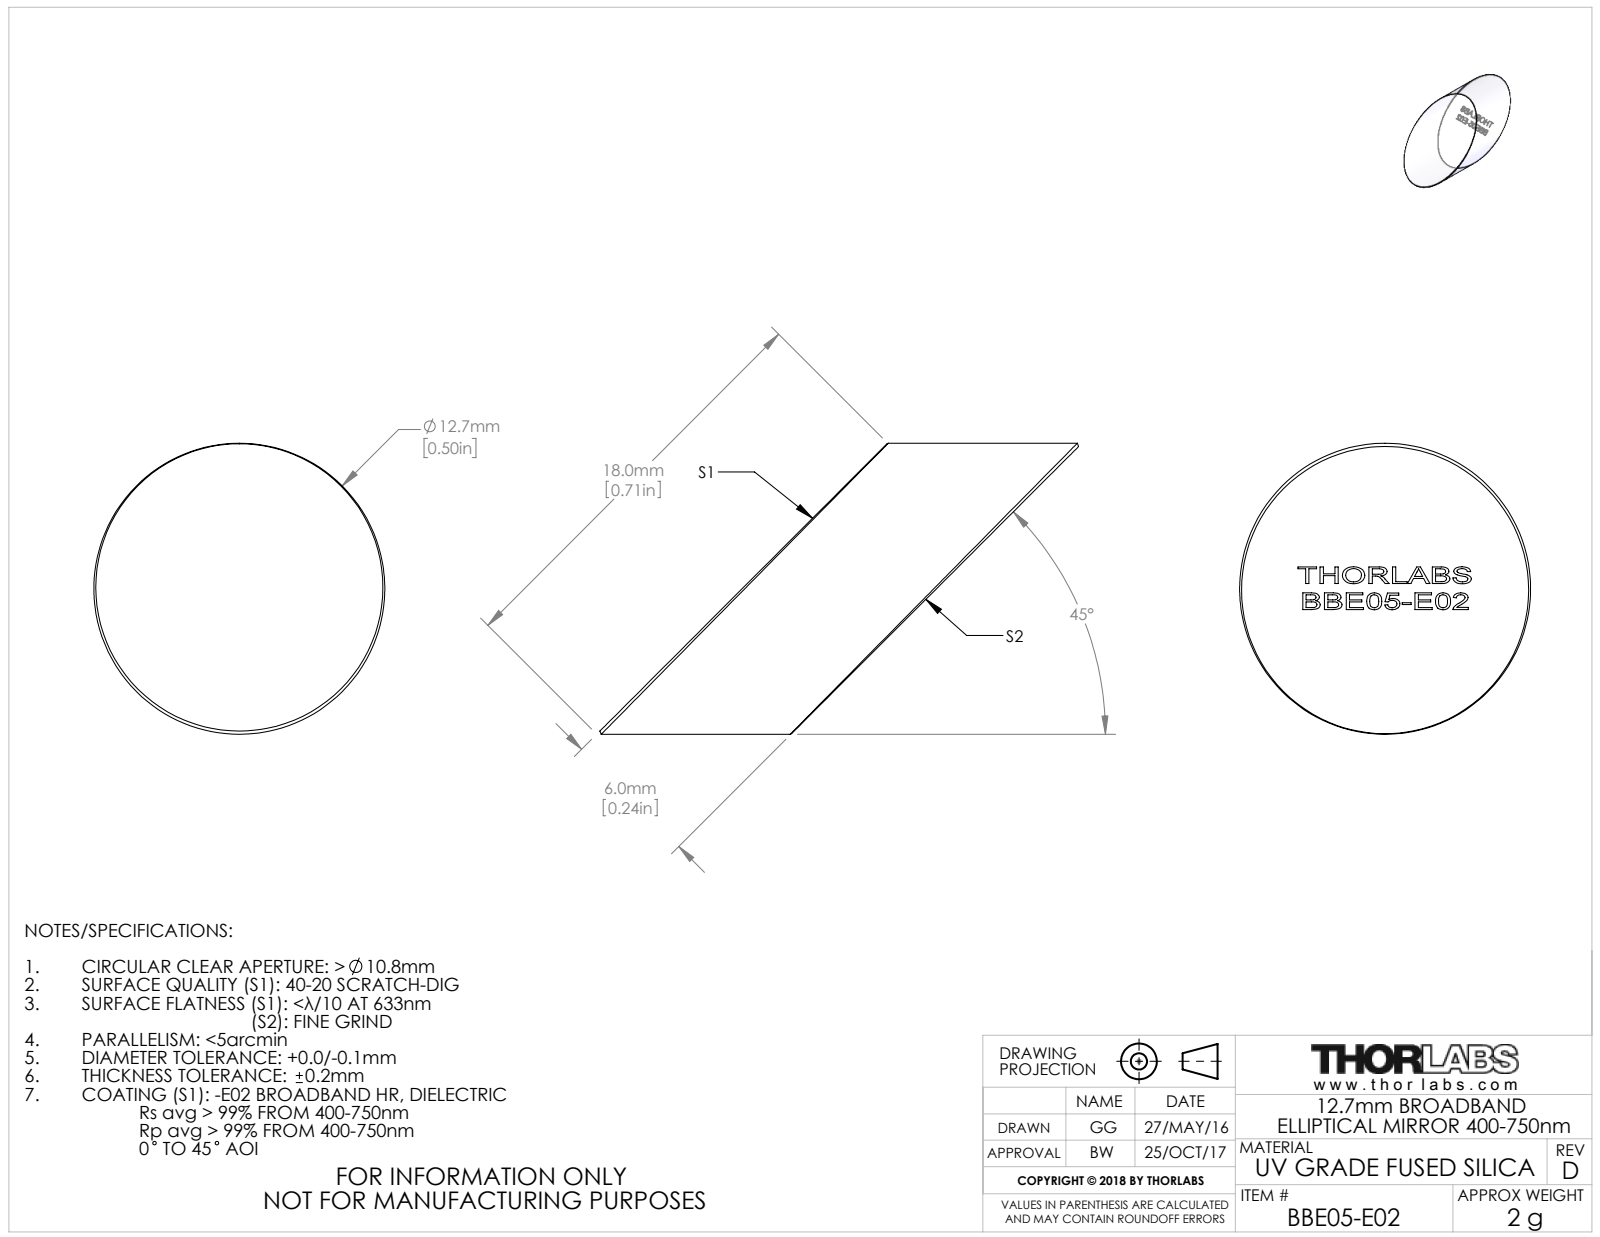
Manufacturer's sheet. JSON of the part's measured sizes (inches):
{"part_name": "21545-E0W", "step_written_by": "SolidWorks 2016 (CONFIG_CONTROL_DESIGN)", "units": "inches", "bodies": {"solids": 1, "faces": 36, "planar": 30, "cylindrical": 2, "other": 4}, "overall_size": [0.823, 0.5, 0.5], "volume_in3": 0.066, "surface_area_in2": 1.068, "round_bosses_or_shafts": [[0.5, 1]], "face_to_face_distances": [0.236]}
